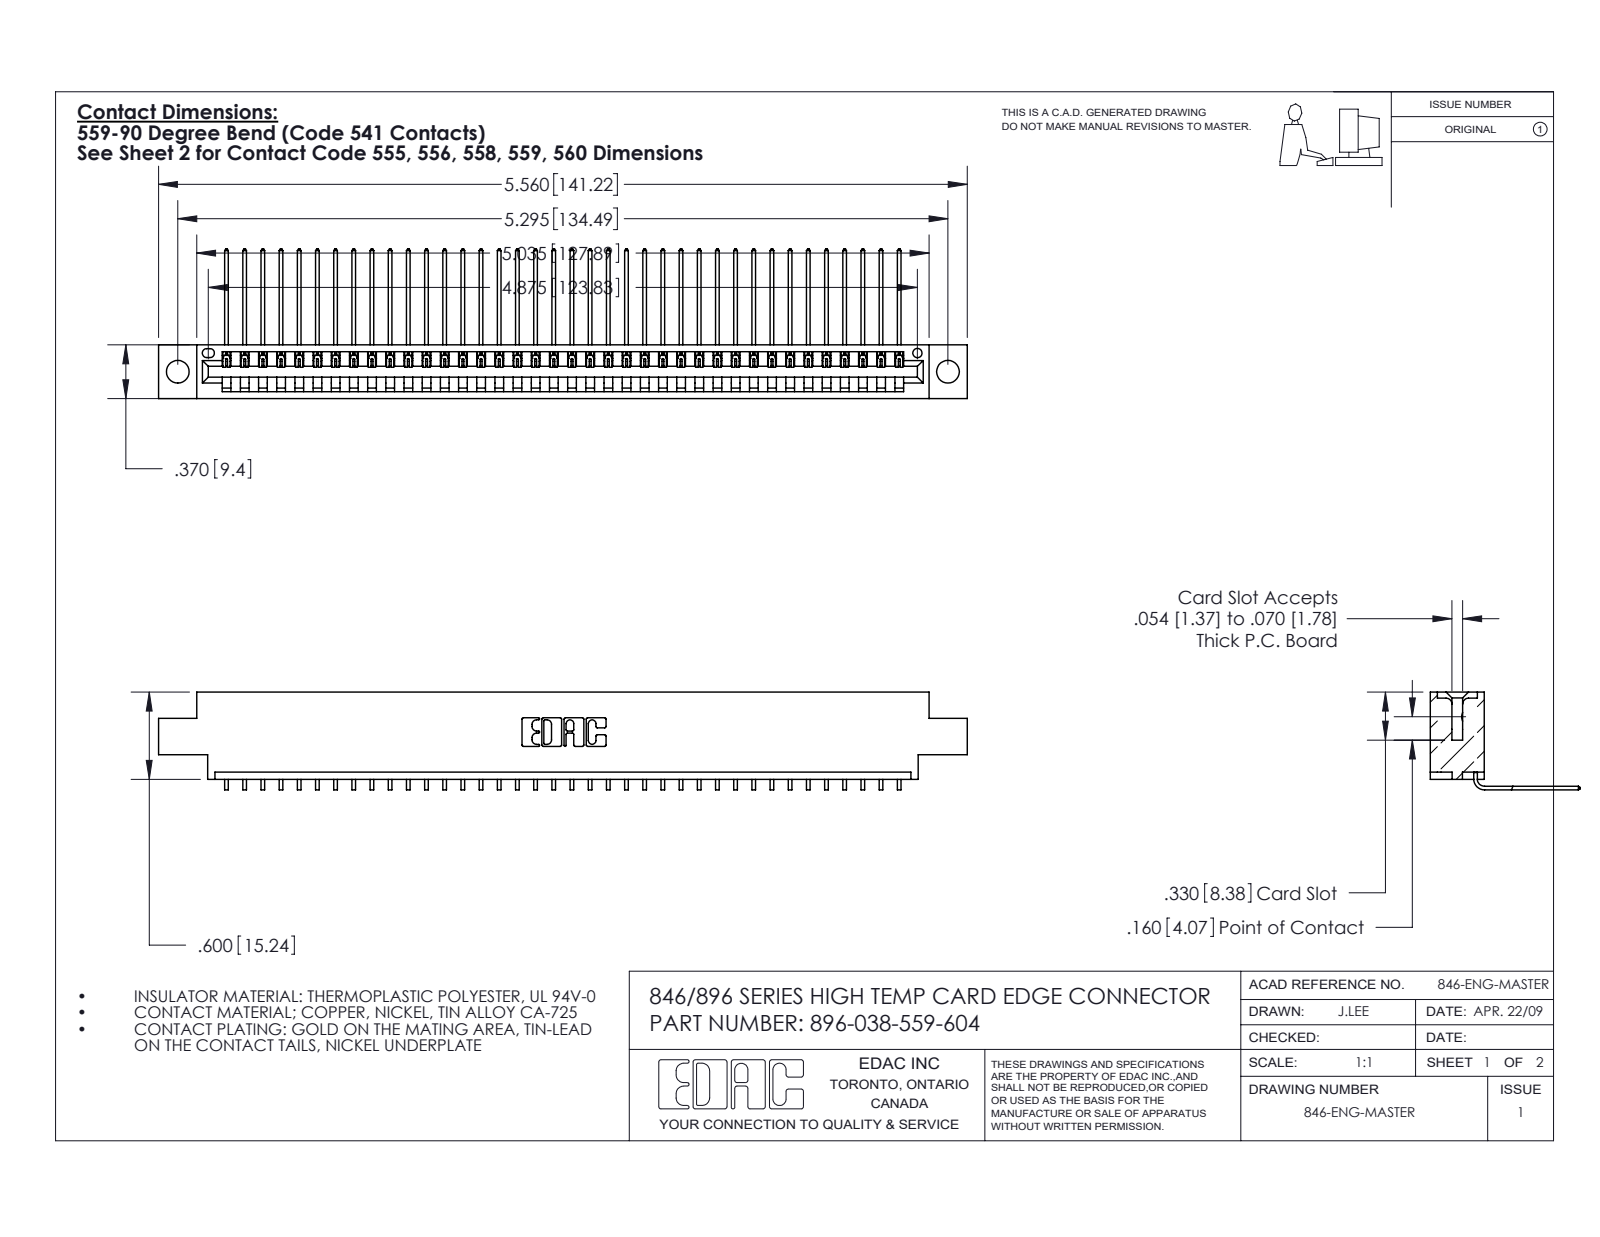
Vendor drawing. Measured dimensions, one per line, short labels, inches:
name: 346 Part_0.170 Offset - 0.156 Dia-TH; 345-292-001_558 559 Tail - 1; 396-038-559-604
written by: SolidWorks 2016 (CONFIG_CONTROL_DESIGN)
unit: in
bodies: 39 solids, 2406 faces (1676 planar, 730 cylindrical, 0 other)
size: 5.56 × 1.03 × 0.673
volume: 0.816 in³; area: 26.96 in²
holes: 2× ⌀0.156, 1× ⌀0.064
rounds: 76× R0.006, 22× R0.01, 6× R0.007, 6× R0.031, 3× R0.026, 2× R0.031, 2× R0.04, 1× R0.014
face distances: 0.048, 0.322, 0.37, 0.025, 0.25, 0.072, 0.298, 0.148, 0.222, 0.1
hole spacings: 0.246, 5.086, 5.295
